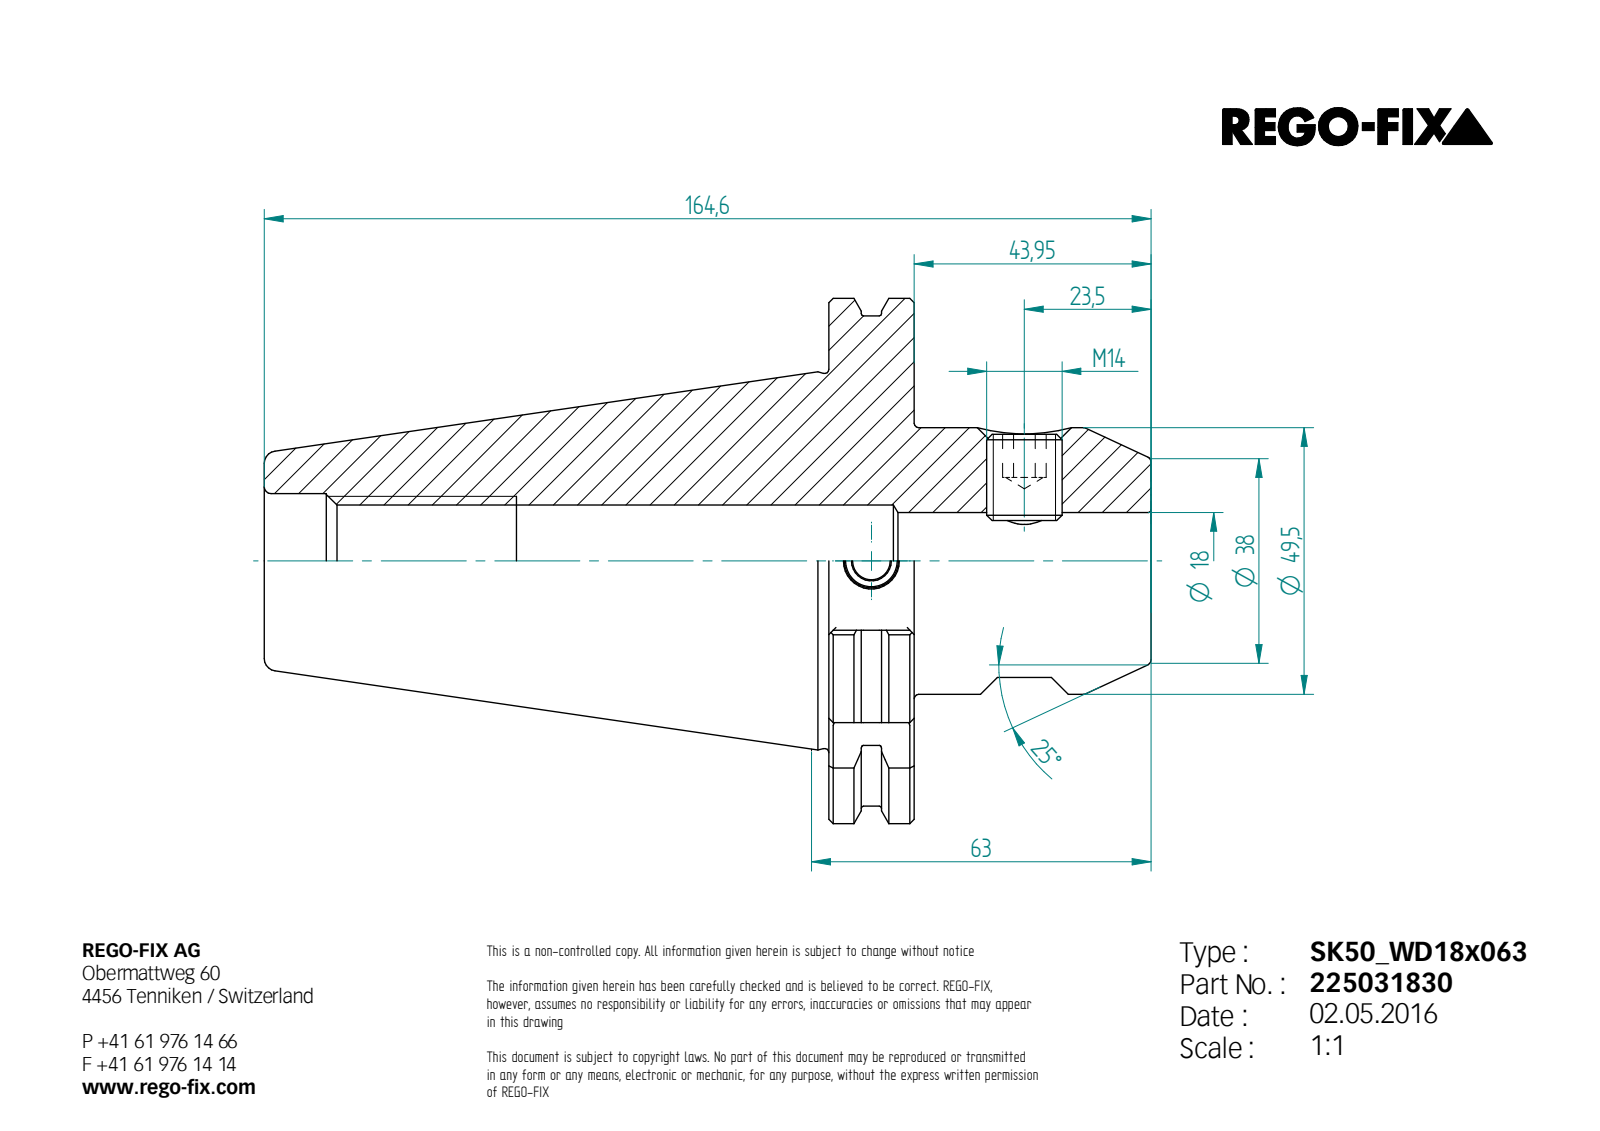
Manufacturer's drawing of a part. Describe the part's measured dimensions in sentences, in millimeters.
Its 3-D file was written by "Unknown (AUTOMOTIVE_DESIGN)". It is 2 solids with 119 faces: 58 planar, 23 cylindrical and 38 other. Overall it measures 164.6 by 97.5 by 93.58 millimeters. Its volume is 388 804 cubic millimeters and its surface area 53 006 square millimeters. Round holes: 1 of diameter 7, 1 of diameter 10, 1 of diameter 11.84, 1 of diameter 18, 1 of diameter 20.75, 1 of diameter 25. Round bosses or shafts: 1 of diameter 91, 1 of diameter 49.5, 1 of diameter 14. Partial cylindrical surfaces (rounded edges, fillets, slot ends): 5 of radius 0.5, 1 of radius 48.75. The main face-to-face distances are 15.85, 59.8, 43.95, 104.8, 120.65, 164.6, 72.8, 25.7, 8.75, 34.45.
